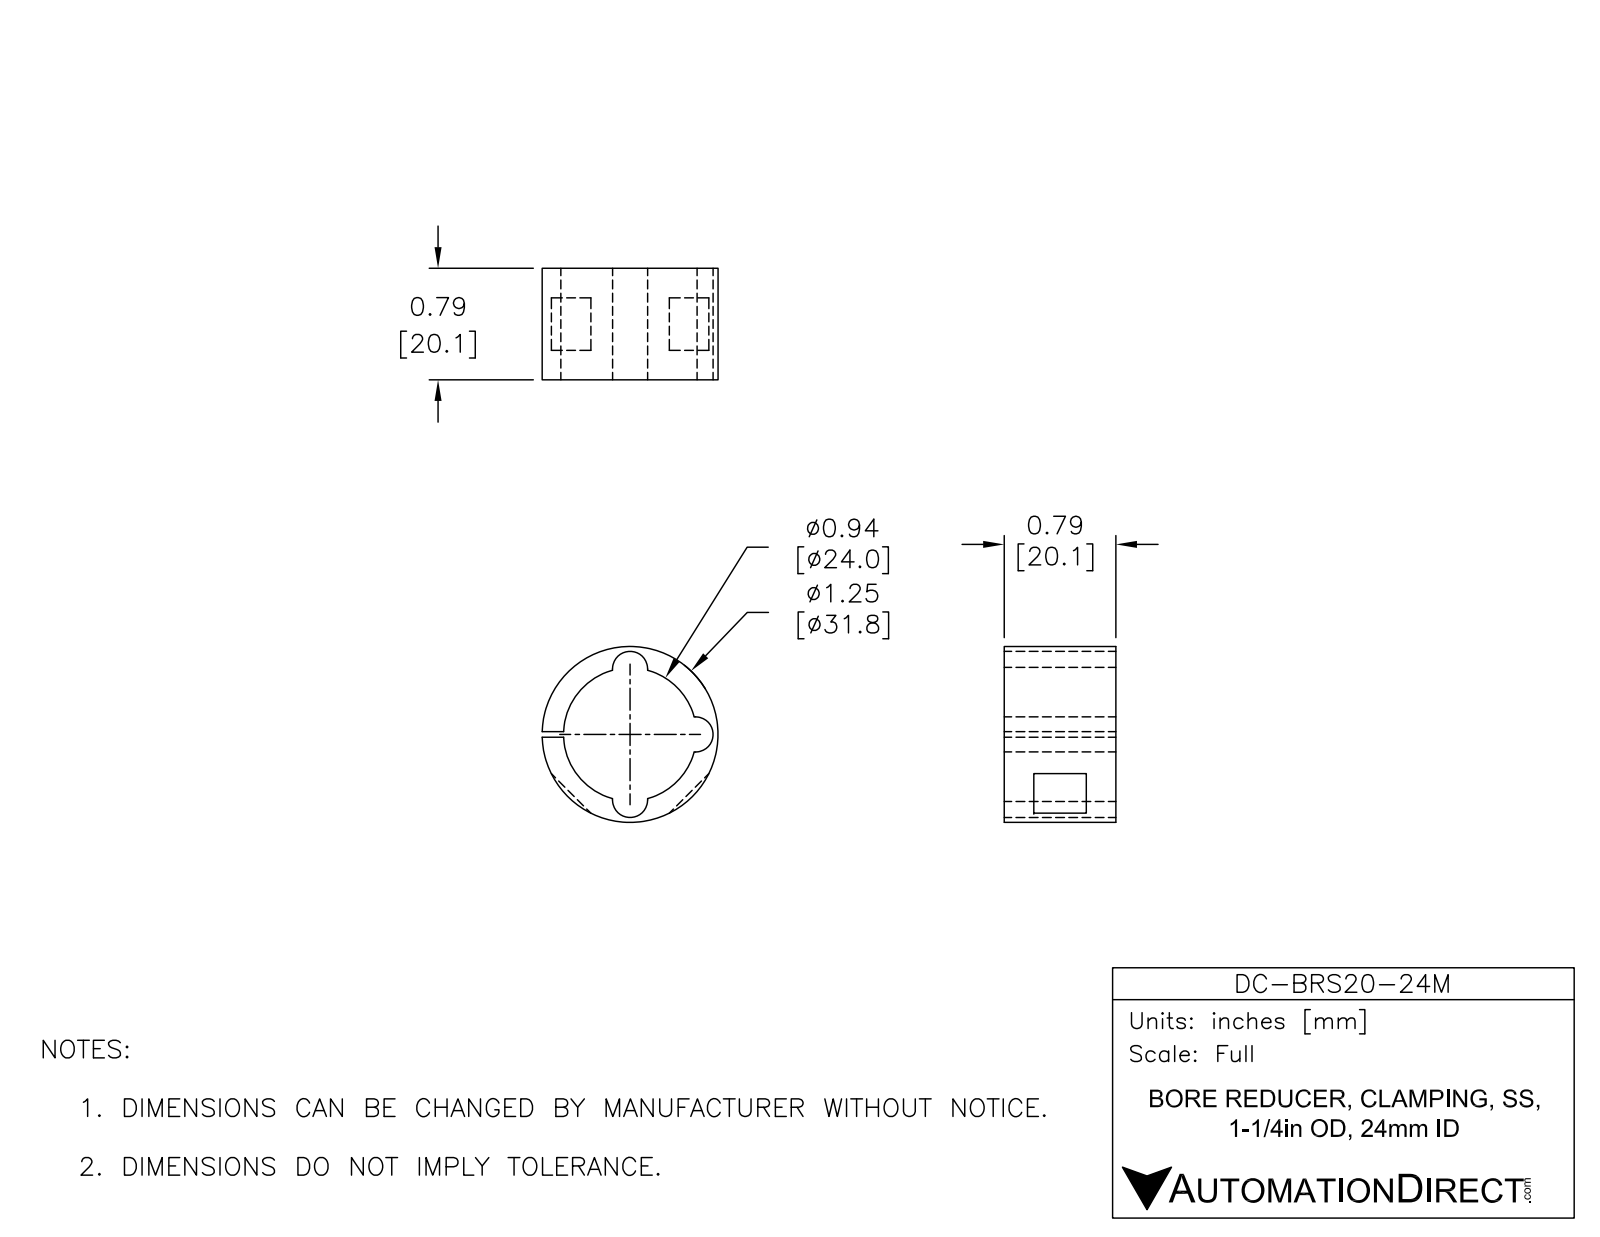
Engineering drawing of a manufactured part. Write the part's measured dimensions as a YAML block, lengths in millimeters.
part_name: "DC-BRS20-24M"
step_written_by: "SolidWorks 2015 (AUTOMOTIVE_DESIGN)"
units: millimeters
bodies: {solids: 1, faces: 20, planar: 10, cylindrical: 10, other: 0}
overall_size: [31.75, 31.74, 20.14]
volume: 5141
surface_area: 4408
round_bosses_or_shafts:
  - {diameter: 31.75, count: 1}
partial_cylinders:
  - {radius: 3.17, count: 3}
  - {radius: 12.5, count: 1}
face_to_face_distances: [20.14, 1.02, 5.33, 14.81, 9.48]
